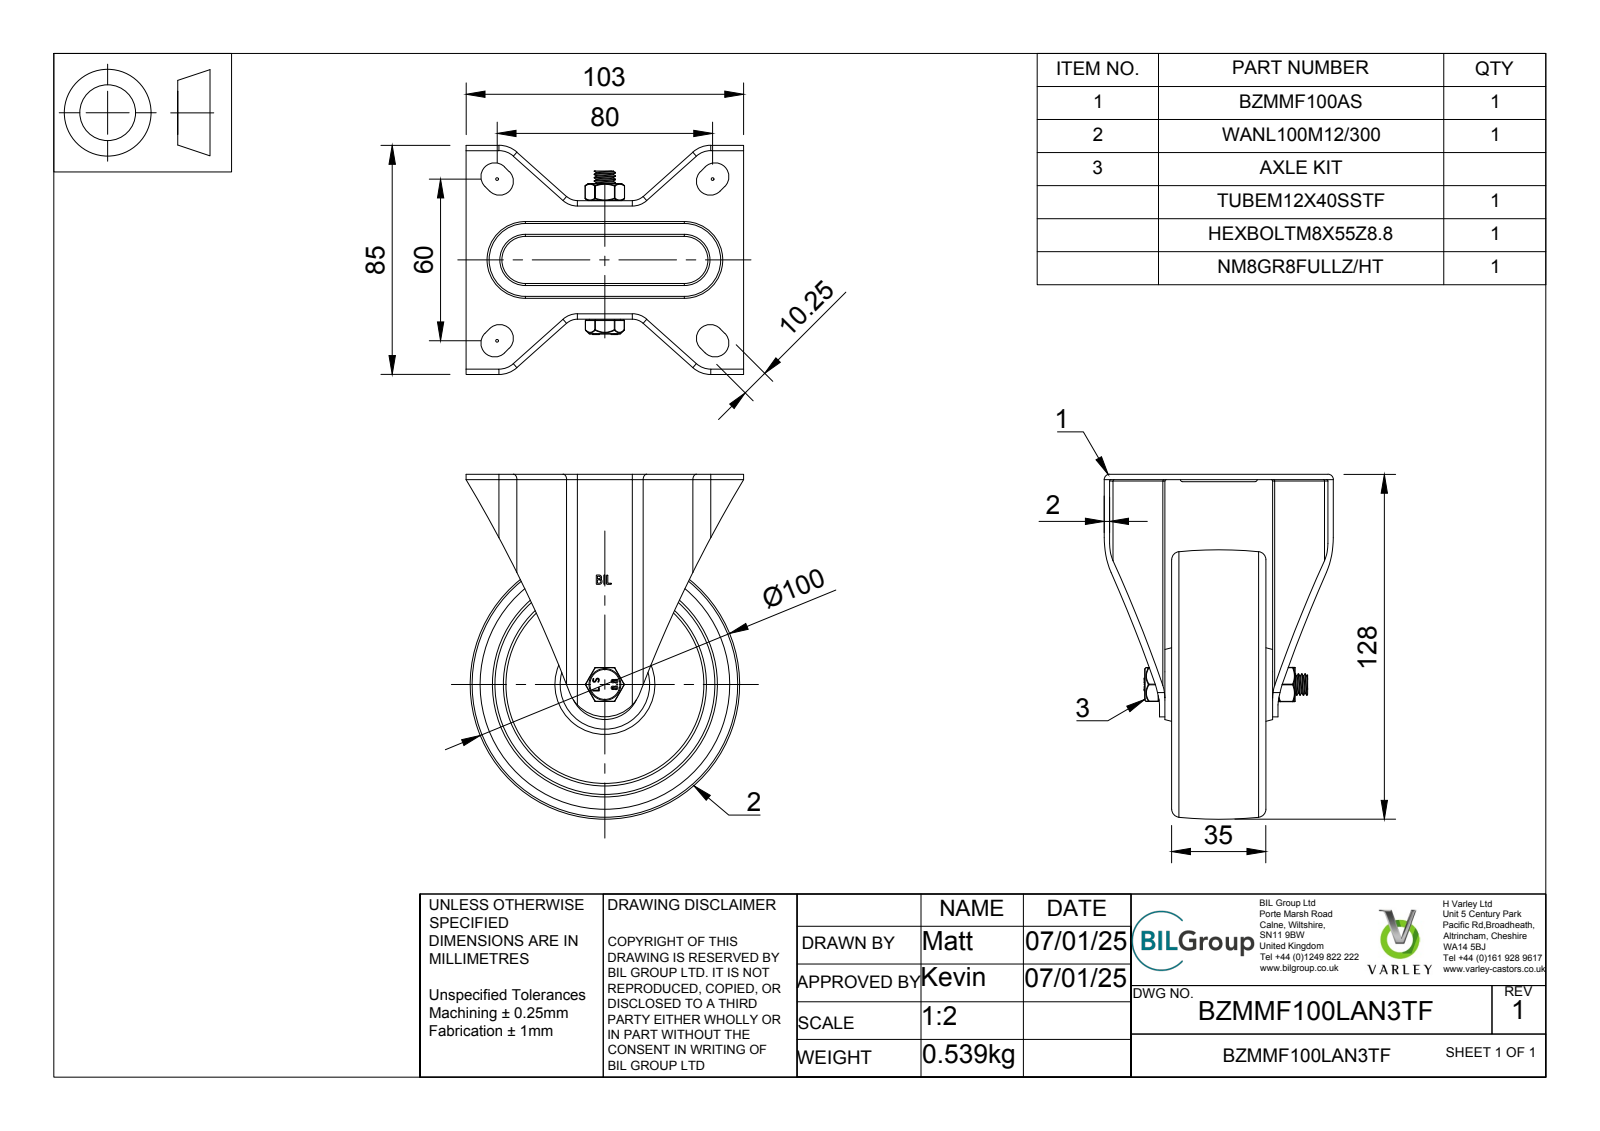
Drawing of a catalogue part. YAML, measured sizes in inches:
part_name: "BZMMF100LAN3TF v3; BZMMF100AS v1; BZMMF100AS; ZINC PLATED, PRESSED STEEL BRACKET (+8 more)"
step_written_by: "Autodesk Translation Framework v13.20.0.188 (AP242_MANAGED_MODEL_BASED_3D_ENGINEERING_MIM_LF)"
units: inches
bodies: {solids: 6, faces: 393, planar: 117, cylindrical: 146, other: 130}
overall_size: [5.039, 4.055, 3.346]
volume: 12.43
surface_area: 122.8
round_holes:
  - {diameter: 0.026, count: 2}
  - {diameter: 0.315, count: 1}
  - {diameter: 0.325, count: 1}
  - {diameter: 0.404, count: 1}
  - {diameter: 0.492, count: 1}
round_bosses_or_shafts:
  - {diameter: 0.472, count: 1}
  - {diameter: 0.453, count: 1}
  - {diameter: 0.31, count: 1}
  - {diameter: 0.254, count: 1}
partial_cylinders:
  - {radius: 0.01, count: 18}
  - {radius: 0.02, count: 8}
  - {radius: 0.03, count: 8}
  - {radius: 0.079, count: 8}
  - {radius: 0.202, count: 8}
  - {radius: 0.013, count: 4}
  - {radius: 0.025, count: 4}
  - {radius: 0.118, count: 4}
face_to_face_distances: [0.079, 0.561, 0.61, 0.965, 0.689, 1.043, 1.654, 0.354, 0.483, 0.64]
hole_center_spacings: [0.127, 0.098]
